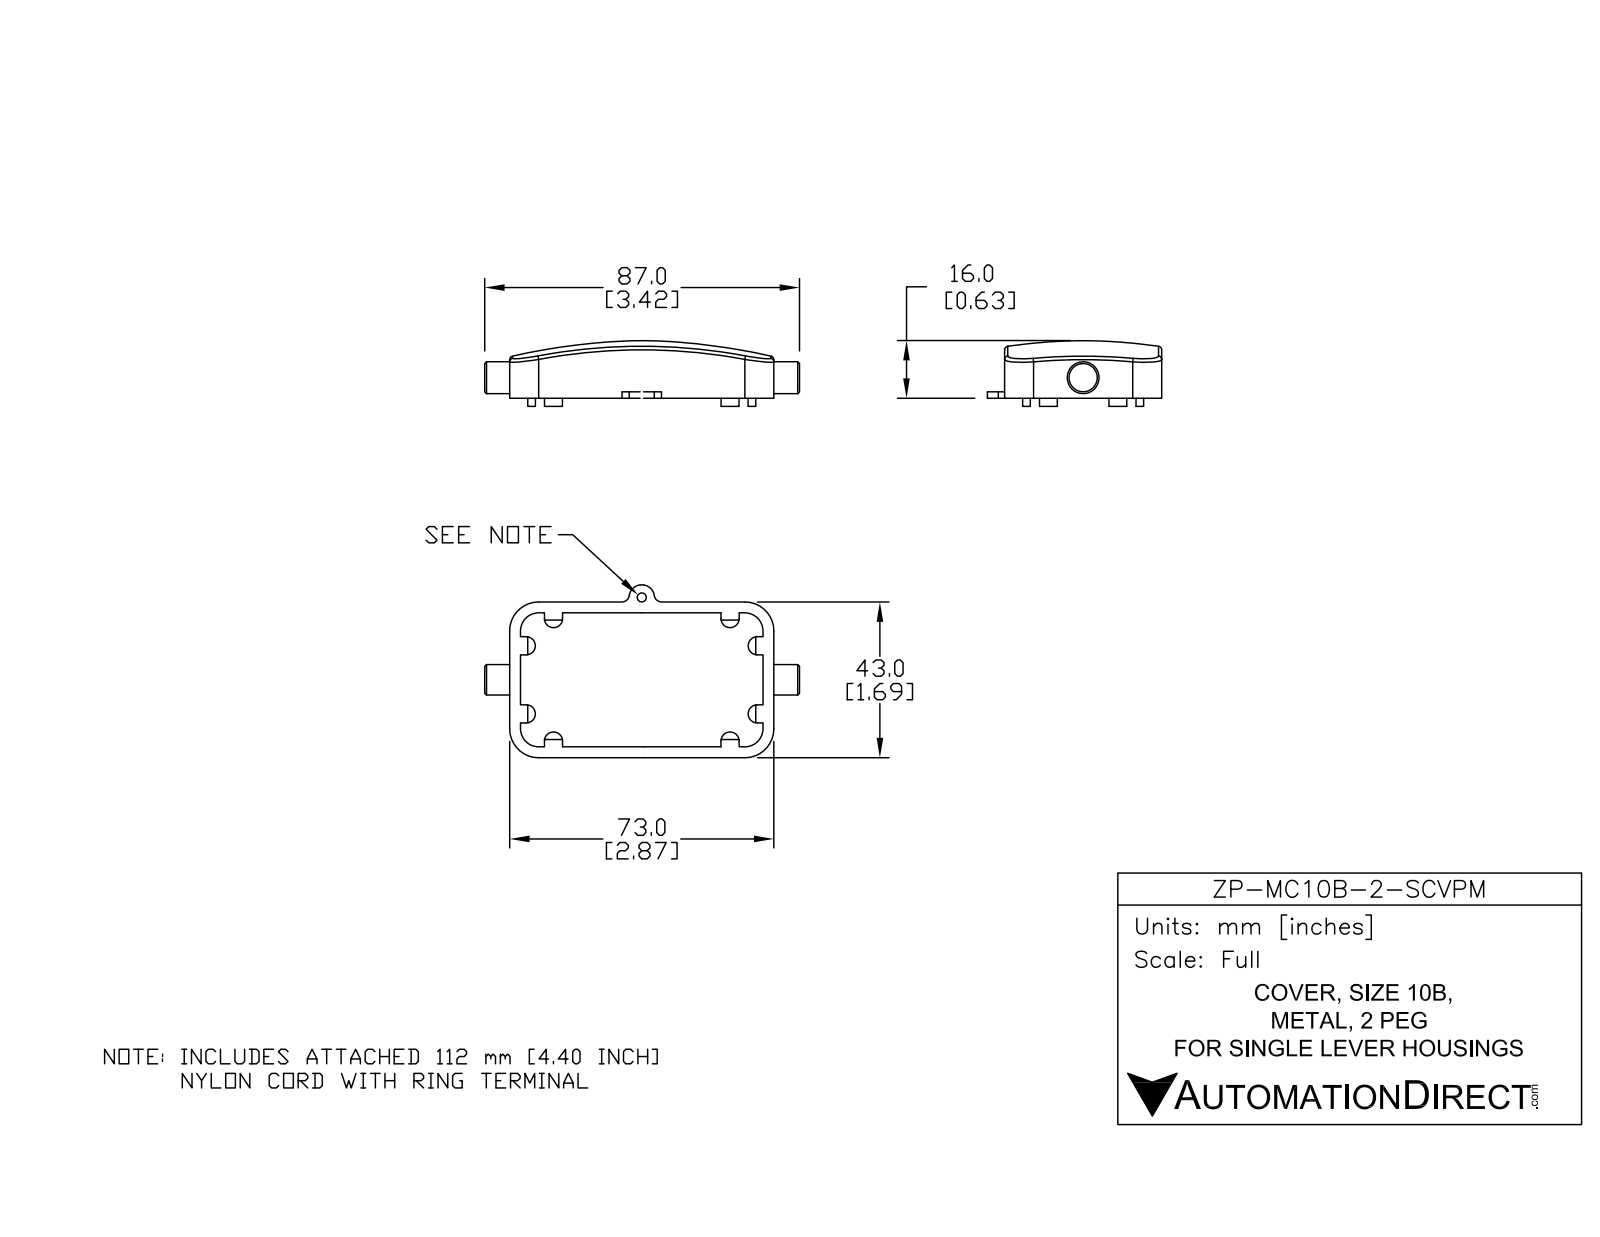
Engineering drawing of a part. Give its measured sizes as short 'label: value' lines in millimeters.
name: ZP-MC10B-2-SCVPM
written by: SolidWorks 2014 (AUTOMOTIVE_DESIGN)
unit: mm
bodies: 4 solids, 129 faces (71 planar, 38 cylindrical, 20 other)
size: 146.44 × 87.16 × 65.35
volume: 18 318 mm³; area: 13 261 mm²
holes: 1× ⌀2.5, 1× ⌀4.1
bosses: 1× ⌀8.8
rounds: 8× R2.5, 4× R0.45, 4× R5, 4× R8, 2× R0.6, 2× R2, 2× R6, 1× R3.5
face distances: 3, 40.4, 43.4, 37.4, 70.38, 73.38, 5, 9.6, 67.38, 14.6
